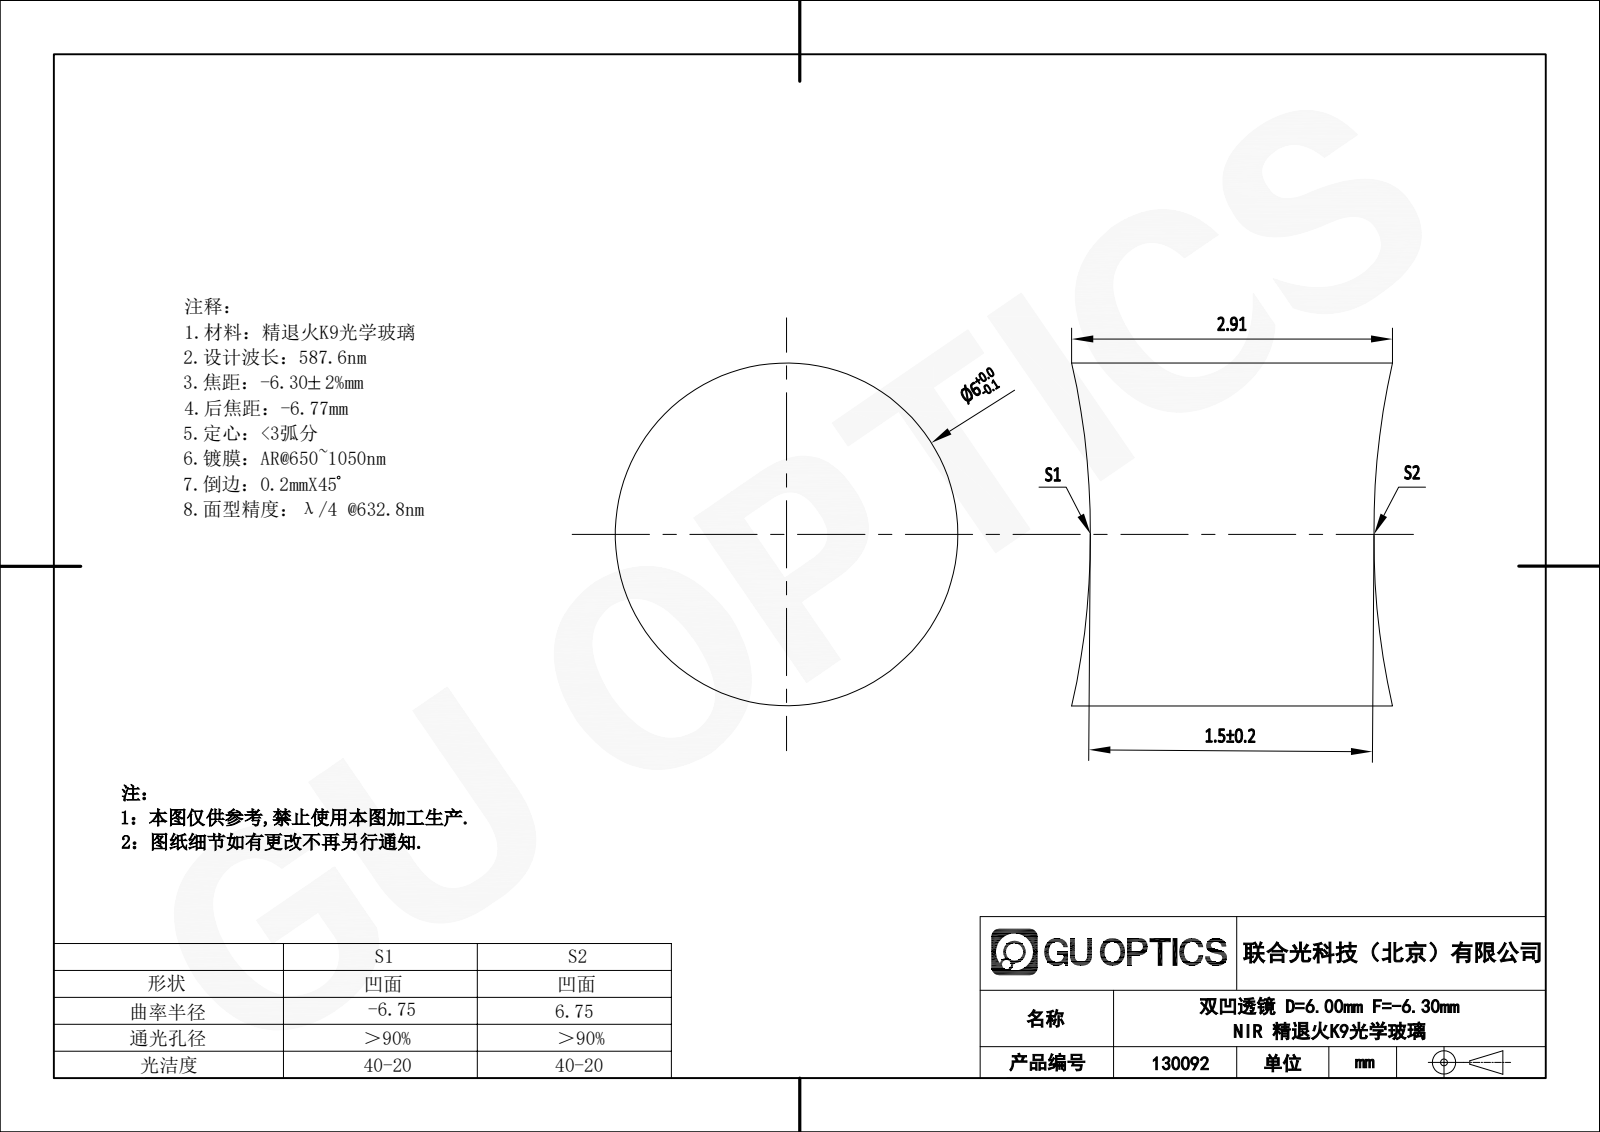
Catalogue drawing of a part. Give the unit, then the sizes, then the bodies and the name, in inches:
Units: inches
Overall size (bounding box): 0.122 × 0.122 × 0.115
Round bosses / shafts (diameter × count): ⌀0.122 ×1
Volume: 0.001 in³ · Surface area: 0.068 in²
Bodies: 1 solid, 6 faces (0 planar, 2 cylindrical, 4 other)
Part name (STEP PRODUCT): xianzhey
STEP written by: SolidWorks 2020 (CONFIG_CONTROL_DESIGN)
